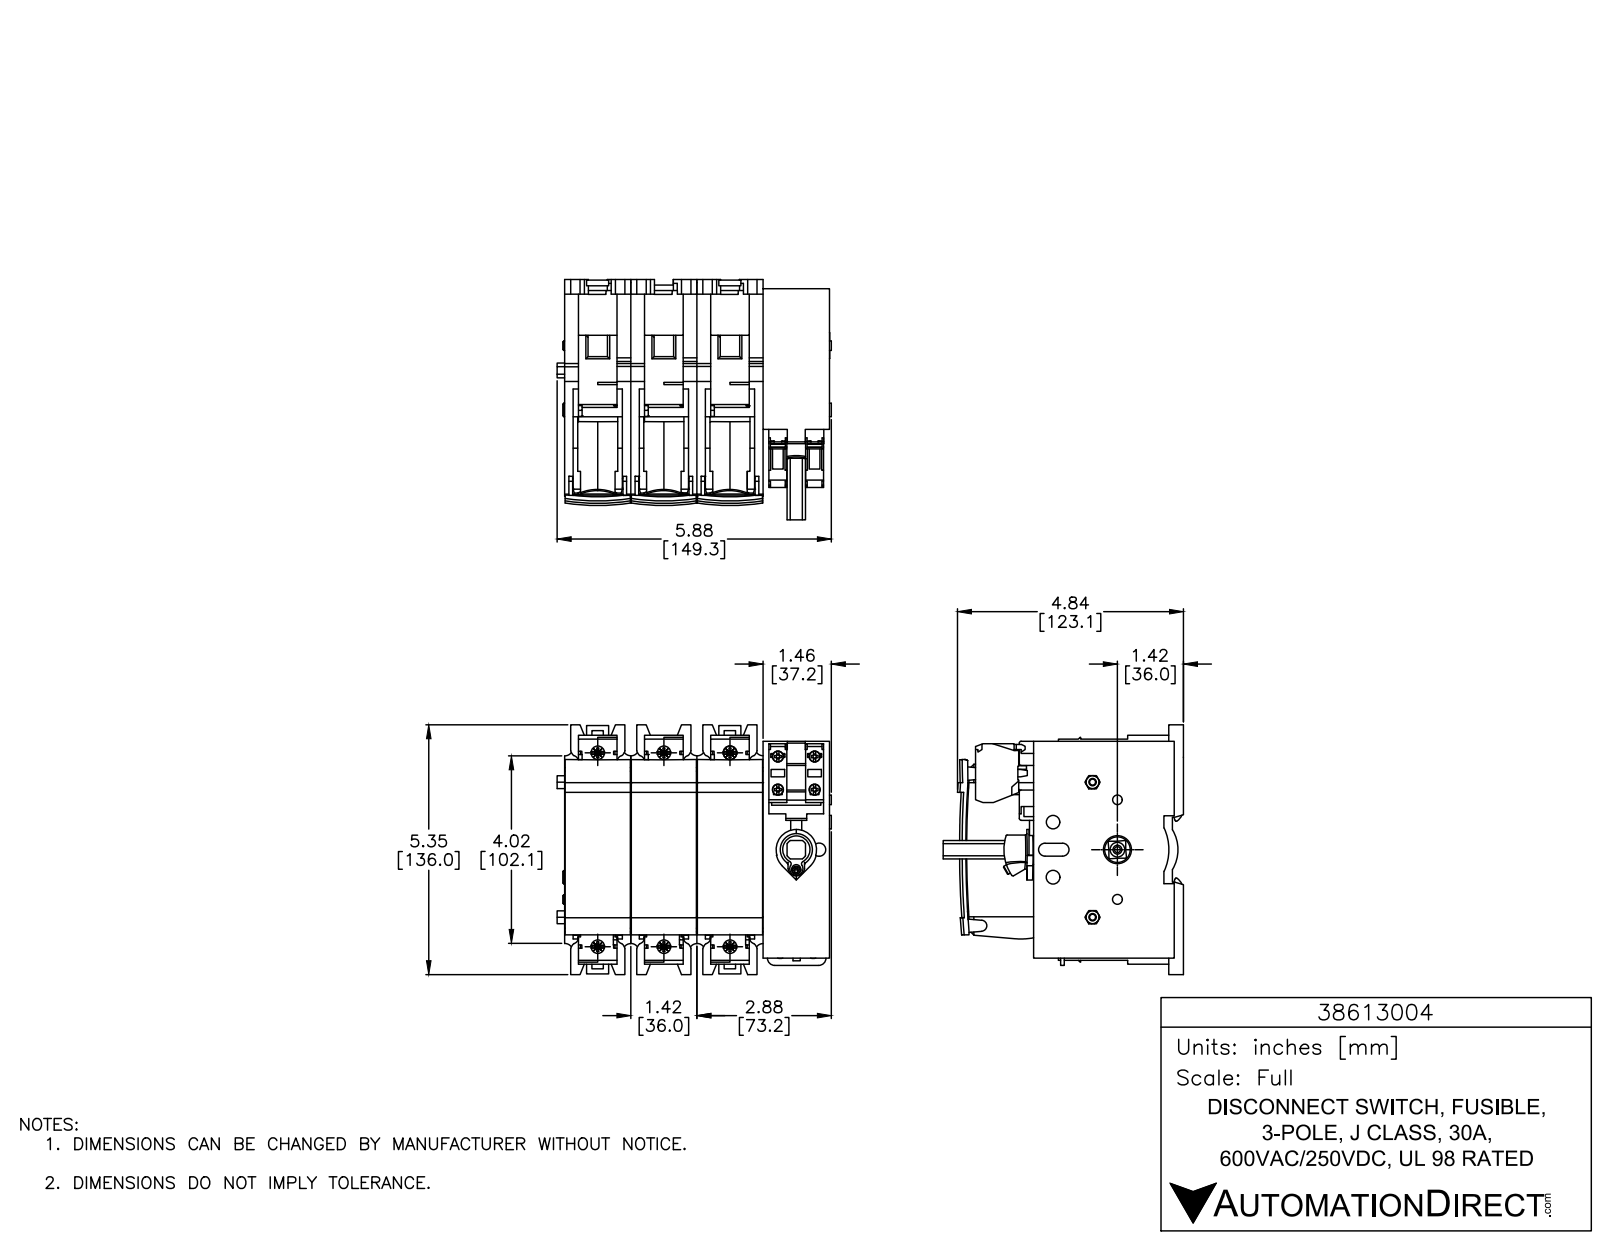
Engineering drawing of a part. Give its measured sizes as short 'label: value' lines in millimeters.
name: 38613004
written by: SolidWorks 2015 (AUTOMOTIVE_DESIGN)
unit: mm
bodies: 13 solids, 2177 faces (1447 planar, 475 cylindrical, 255 other)
size: 149.3 × 136 × 123.1
volume: 1 509 000 mm³; area: 227 400 mm²
holes: 6× ⌀7.4, 2× ⌀2.2, 2× ⌀3.2, 2× ⌀4, 2× ⌀4, 2× ⌀4.3, 2× ⌀5.4, 2× ⌀7.5, 2× ⌀8, 1× ⌀2.5, 1× ⌀3.3, 1× ⌀7.2
bosses: 2× ⌀7.3, 2× ⌀5.2, 1× ⌀16, 1× ⌀8, 1× ⌀5, 1× ⌀3.5
rounds: 68× R0.2, 12× R0.5, 11× R1, 7× R5, 4× R3, 3× R3.5, 2× R1.7, 2× R4
face distances: 36, 72, 7.5, 28.5, 108, 43.5, 64.5, 36.2, 72.2, 108.2
hole spacings: 36, 111.4, 105.4, 16.6, 25.1, 27.1, 30.6, 34.1
